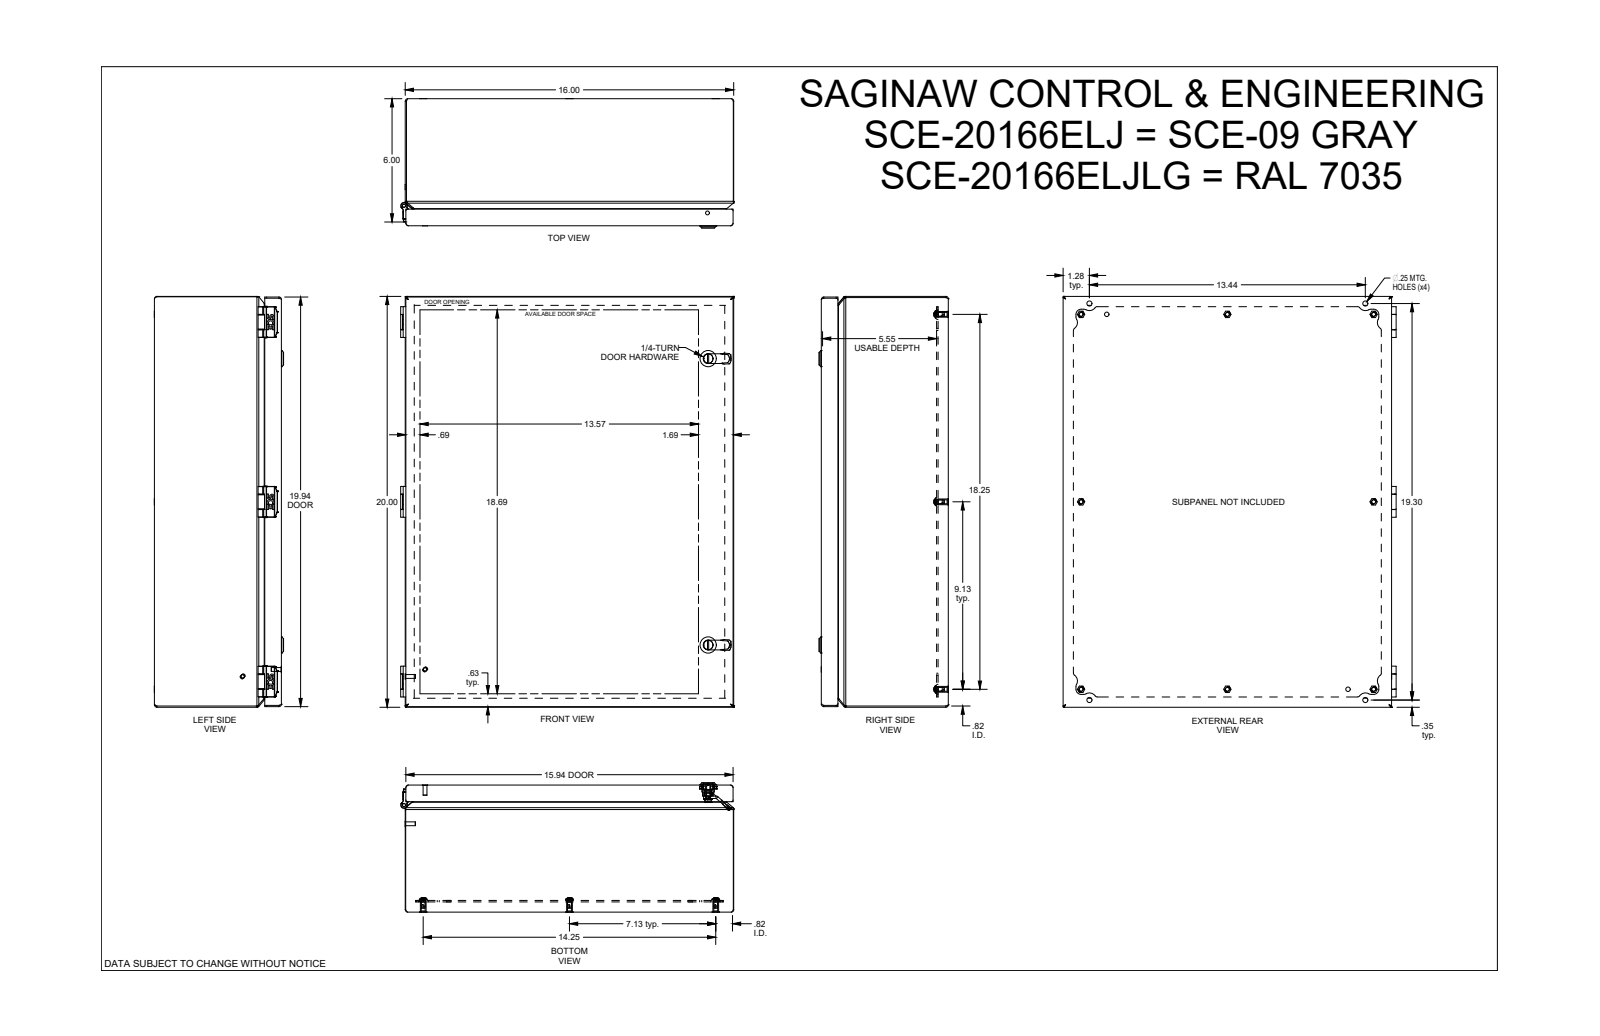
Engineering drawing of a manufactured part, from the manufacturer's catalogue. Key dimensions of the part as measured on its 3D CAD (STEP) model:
Part name (STEP PRODUCT): SCE-20166ELJ
STEP written by: SolidWorks 2021 (AUTOMOTIVE_DESIGN)
Units: inches
Bodies: 36 solids, 2038 faces (647 planar, 581 cylindrical, 810 other)
Overall size (bounding box): 20 × 16.22 × 6.292
Volume: 89.99 in³ · Surface area: 2 861 in²
Round holes (diameter × count): ⌀0.25 ×10, ⌀0.284 ×8, ⌀0.17 ×3, ⌀0.2 ×2, ⌀0.218 ×2, ⌀0.239 ×2, ⌀0.254 ×2, ⌀0.269 ×2, ⌀0.282 ×2, ⌀0.326 ×2, ⌀0.475 ×2, ⌀0.63 ×2
Round bosses / shafts (diameter × count): ⌀0.188 ×9, ⌀0.373 ×8, ⌀0.479 ×3, ⌀0.26 ×3, ⌀0.1 ×3, ⌀0.02 ×3, ⌀0.788 ×2, ⌀0.548 ×2
Partial cylindrical surfaces — rounded edges, fillets, slot ends (radius × count): R0.106 ×99, R0.005 ×51, R0.008 ×48, R0.013 ×31, R0.01 ×18, R0.025 ×18, R0.05 ×16, R0.062 ×12
Main face-to-face distances: 0.059, 0.062, 6.185, 6.126, 6.123, 6.064, 0.571, 0.512, 5.552, 5.614
Hole centre spacings: 7.125, 7.125, 9.125, 14.25, 19.593, 11.577, 11.578, 16.921
